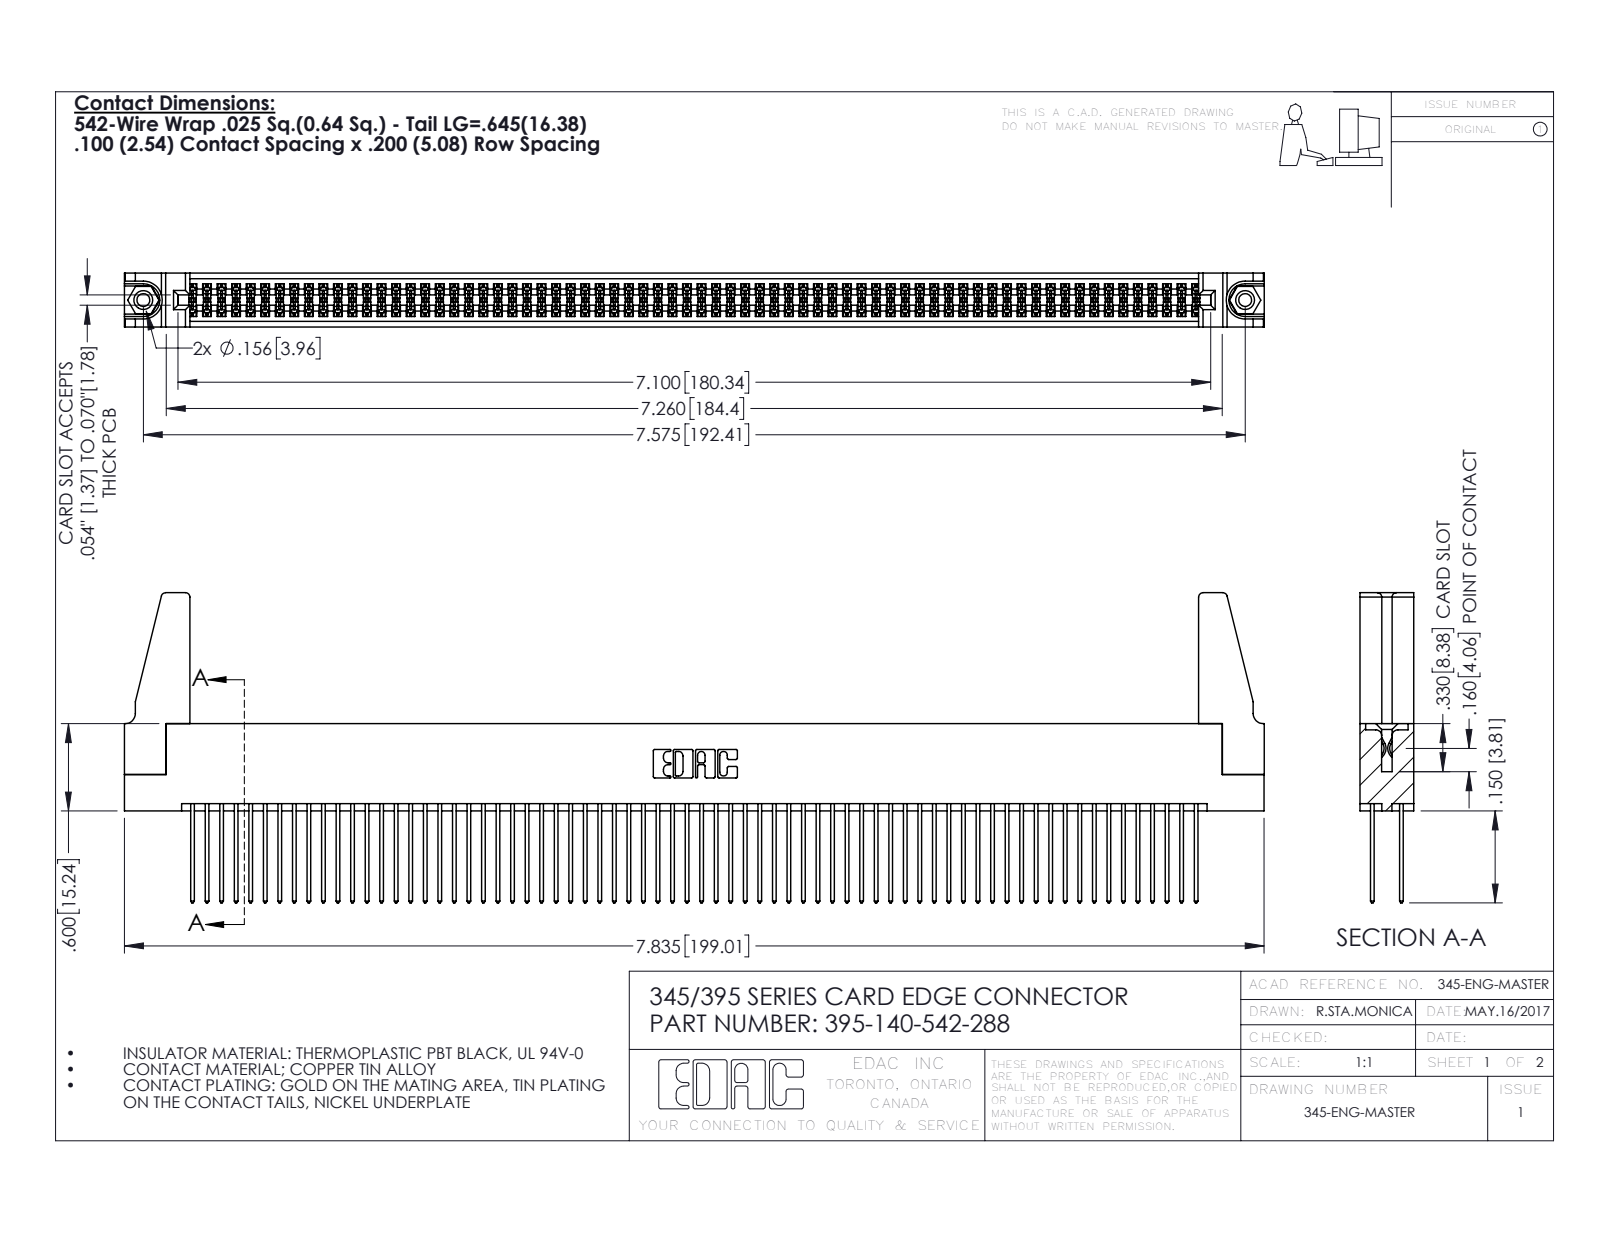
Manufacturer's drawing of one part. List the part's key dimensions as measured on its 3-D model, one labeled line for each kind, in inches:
Part name (STEP PRODUCT): 345-220-078_345-220-088; 345-292-001_345-293-142; 395-140-542-288; 345-250-001_345-250-001-102 (+1 more)
STEP written by: SolidWorks 2016 (CONFIG_CONTROL_DESIGN)
Units: inches
Bodies: 145 solids, 7250 faces (4772 planar, 2462 cylindrical, 16 other)
Overall size (bounding box): 7.836 × 2.132 × 0.37
Volume: 1.434 in³ · Surface area: 56.8 in²
Round holes (diameter × count): ⌀0.089 ×2, ⌀0.125 ×2, ⌀0.156 ×2, ⌀0.064 ×1
Round bosses / shafts (diameter × count): ⌀0.155 ×2
Partial cylindrical surfaces — rounded edges, fillets, slot ends (radius × count): R0.006 ×210, R0.01 ×140, R0.01 ×22, R0.03 ×8, R0.007 ×6, R0.031 ×6, R0.026 ×3, R0.014 ×2
Main face-to-face distances: 0.072, 0.298, 0.2, 0.098, 0.272, 0.025, 0.37, 0.225, 0.175, 0.149
Hole centre spacings: 0.27, 7.339, 7.575
